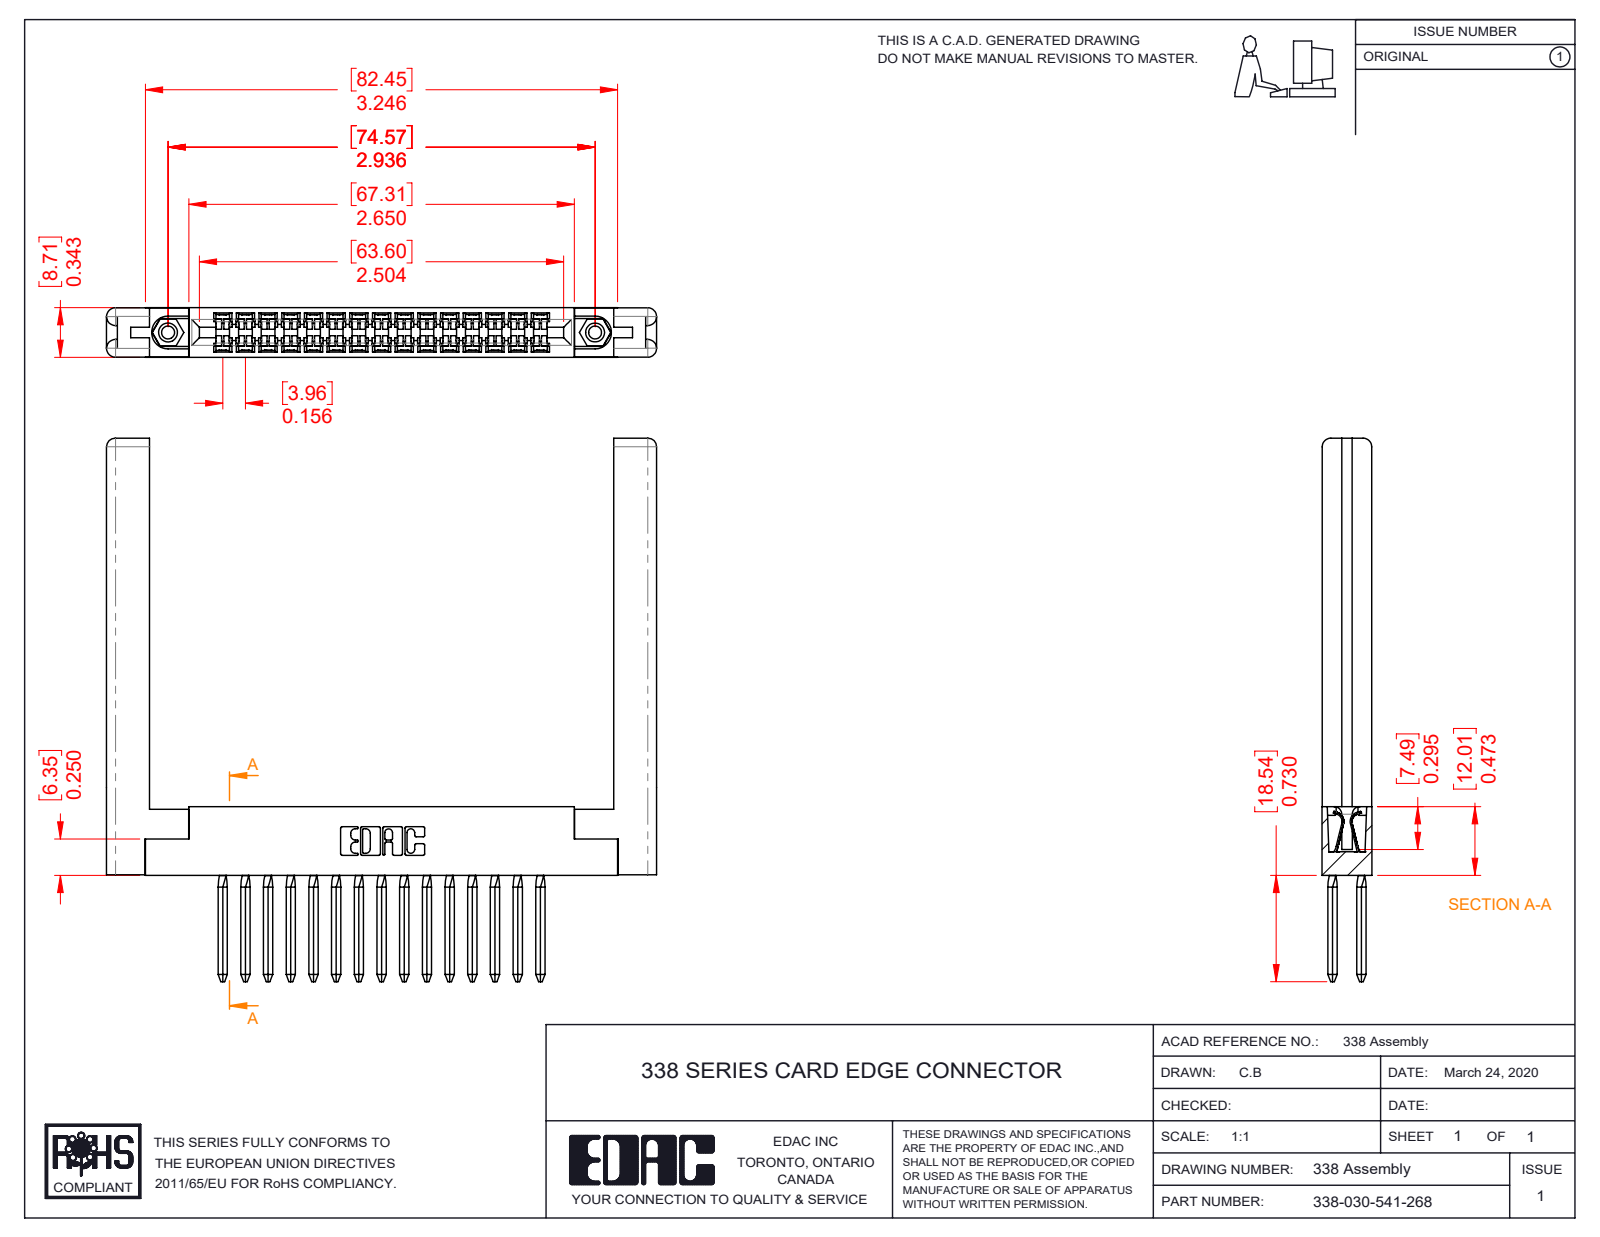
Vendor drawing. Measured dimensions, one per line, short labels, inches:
name: 345-250-001_345-250-001-102; 338-290-001_541; 307-220-058; 338-210-001_338-210-015-004 (+1 more)
written by: SolidWorks 2016 (CONFIG_CONTROL_DESIGN)
unit: in
bodies: 35 solids, 2246 faces (1544 planar, 558 cylindrical, 144 other)
size: 3.782 × 3.735 × 0.343
volume: 0.905 in³; area: 27.61 in²
holes: 2× ⌀0.089, 2× ⌀0.125, 2× ⌀0.156
bosses: 2× ⌀0.155
rounds: 92× R0.025, 30× R0.008, 24× R0.055, 24× R0.067, 24× R0.1, 22× R0.01, 8× R0.061, 6× R0.007
face distances: 0.341, 0.34, 0.136, 0.343, 0.207, 0.134, 0.206, 0.22, 3.192, 0.071
hole spacings: 2.936
